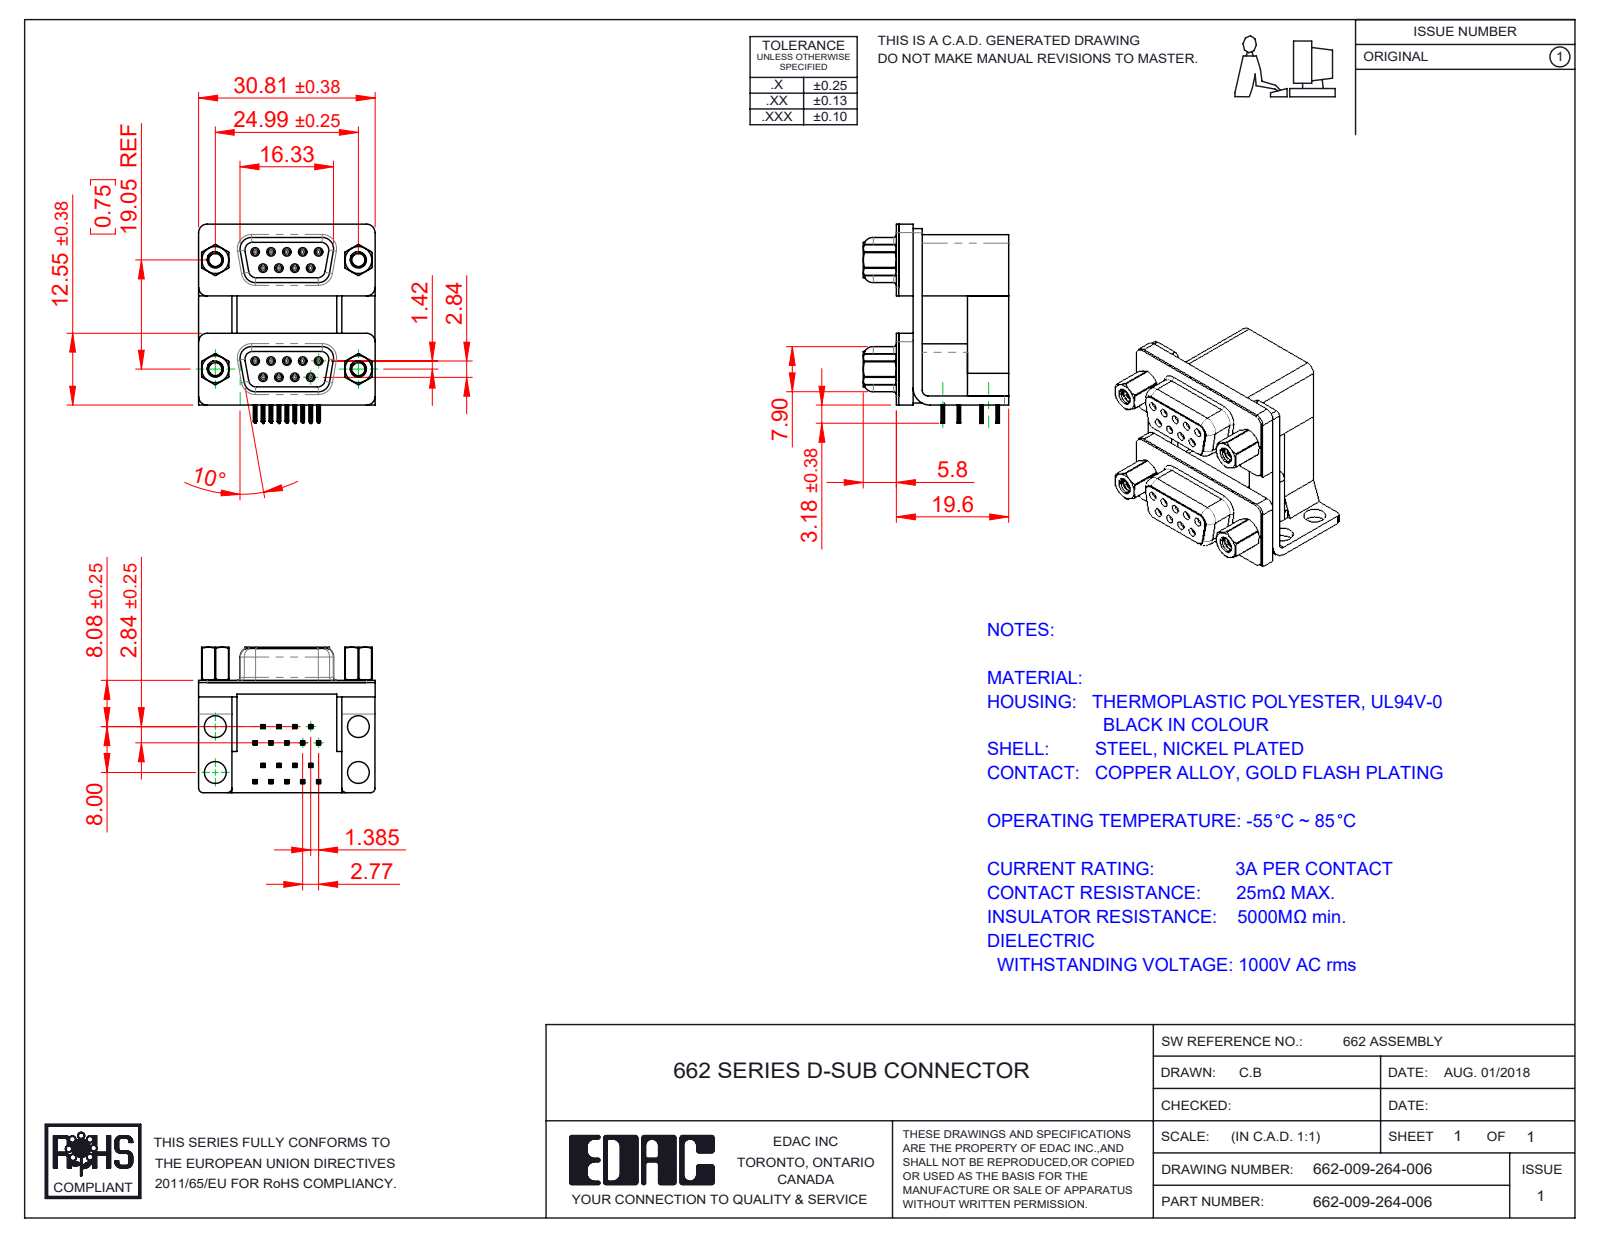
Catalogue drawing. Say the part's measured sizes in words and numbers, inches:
The part is named "662 Housing Spacer_09 Contacts M; 662 Shell_09 Contacts; 662 Contact Top Upper_M; 662 Mounting Bracket_NoneM (+8 more)". Its 3-D file was written by "SolidWorks 2020 (CONFIG_CONTROL_DESIGN)". It is 33 solids with 3362 faces: 1418 planar, 940 cylindrical and 1004 other. Overall it measures 1.369 by 1.213 by 1 inches. Its volume is 0.714 cubic inches and its surface area 21.91 square inches. Round holes: 18 of diameter 0.031, 18 of diameter 0.035, 4 of diameter 0.089, 4 of diameter 0.09, 4 of diameter 0.138, 4 of diameter 0.15, 4 of diameter 0.157, 4 of diameter 0.189, 4 of diameter 0.197. Round bosses or shafts: 18 of diameter 0.047, 4 of diameter 0.193, 4 of diameter 0.187, 4 of diameter 0.154, 4 of diameter 0.11. Partial cylindrical surfaces (rounded edges, fillets, slot ends): 144 of radius 0.004, 72 of radius 0.006, 36 of radius 0.014, 18 of radius 0.013, 16 of radius 0.053, 12 of radius 0.059, 8 of radius 0.011, 8 of radius 0.02. The main face-to-face distances are 0.016, 0.098, 0.657, 0.756, 0.75, 0.114, 0.472, 0.488, 0.772, 0.283. The hole center spacings are 0.124, 0.758, 0.109, 0.75, 0.781, 0.863, 0.218, 0.877.
